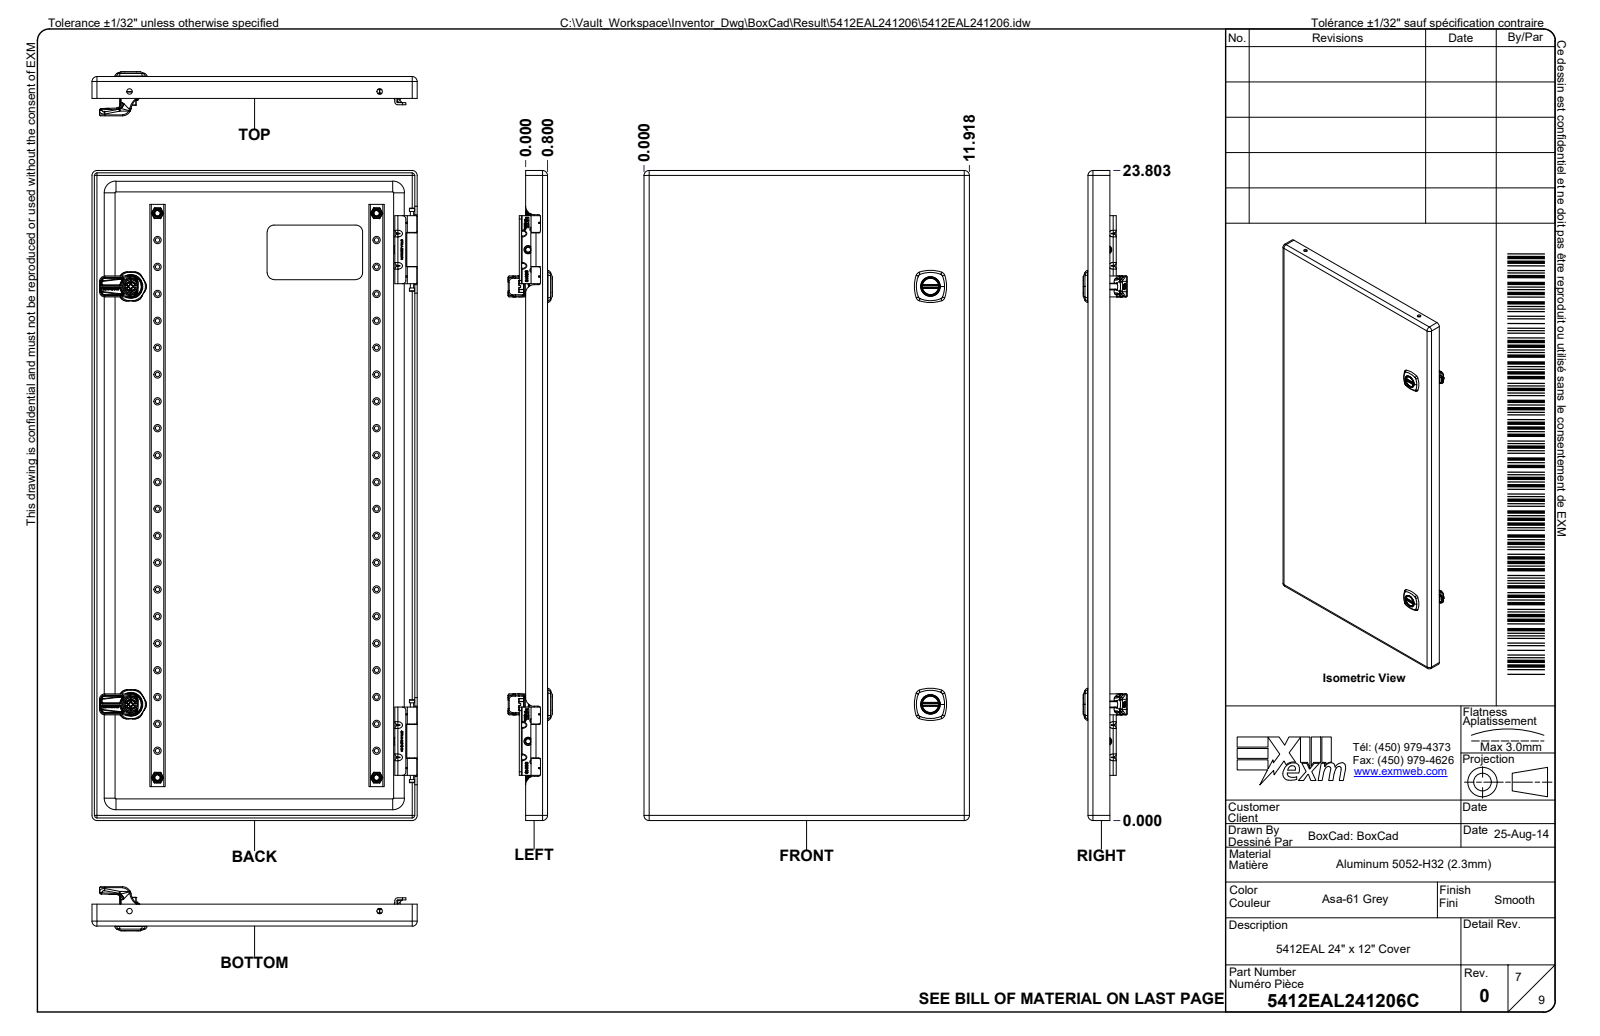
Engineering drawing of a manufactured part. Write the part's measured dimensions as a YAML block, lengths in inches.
part_name: "5412EAL241206; 5412EAL241206B; 5412EAL241206B-P; STK-Q-16010 (+8 more)"
step_written_by: "Autodesk Inventor 2024 (AUTOMOTIVE_DESIGN)"
units: inches
bodies: {solids: 64, faces: 6056, planar: 2855, cylindrical: 1237, other: 1964}
overall_size: [24, 12.042, 7.239]
volume: 141.6
surface_area: 3163
round_holes:
  - {diameter: 0.165, count: 40}
  - {diameter: 0.03, count: 9}
  - {diameter: 0.201, count: 8}
  - {diameter: 0.29, count: 6}
  - {diameter: 0.311, count: 6}
  - {diameter: 0.315, count: 6}
  - {diameter: 0.044, count: 4}
  - {diameter: 0.197, count: 4}
  - {diameter: 0.268, count: 4}
  - {diameter: 0.27, count: 4}
  - {diameter: 0.39, count: 4}
  - {diameter: 0.5, count: 4}
round_bosses_or_shafts:
  - {diameter: 0.237, count: 40}
  - {diameter: 0.232, count: 9}
  - {diameter: 0.03, count: 9}
  - {diameter: 0.039, count: 8}
  - {diameter: 0.374, count: 4}
  - {diameter: 0.311, count: 4}
  - {diameter: 0.776, count: 2}
  - {diameter: 0.768, count: 2}
partial_cylinders:
  - {radius: 0.02, count: 106}
  - {radius: 0.039, count: 72}
  - {radius: 0.008, count: 68}
  - {radius: 0.012, count: 50}
  - {radius: 0.031, count: 38}
  - {radius: 0.01, count: 28}
  - {radius: 0.125, count: 27}
  - {radius: 0.121, count: 24}
face_to_face_distances: [0.09, 6.978, 6.888, 11.91, 7.068, 0.964, 0.874, 6.014, 6.104, 0.105]
hole_center_spacings: [0.984, 1.969, 2.953, 3.937, 4.921, 5.906, 6.89, 7.874]
